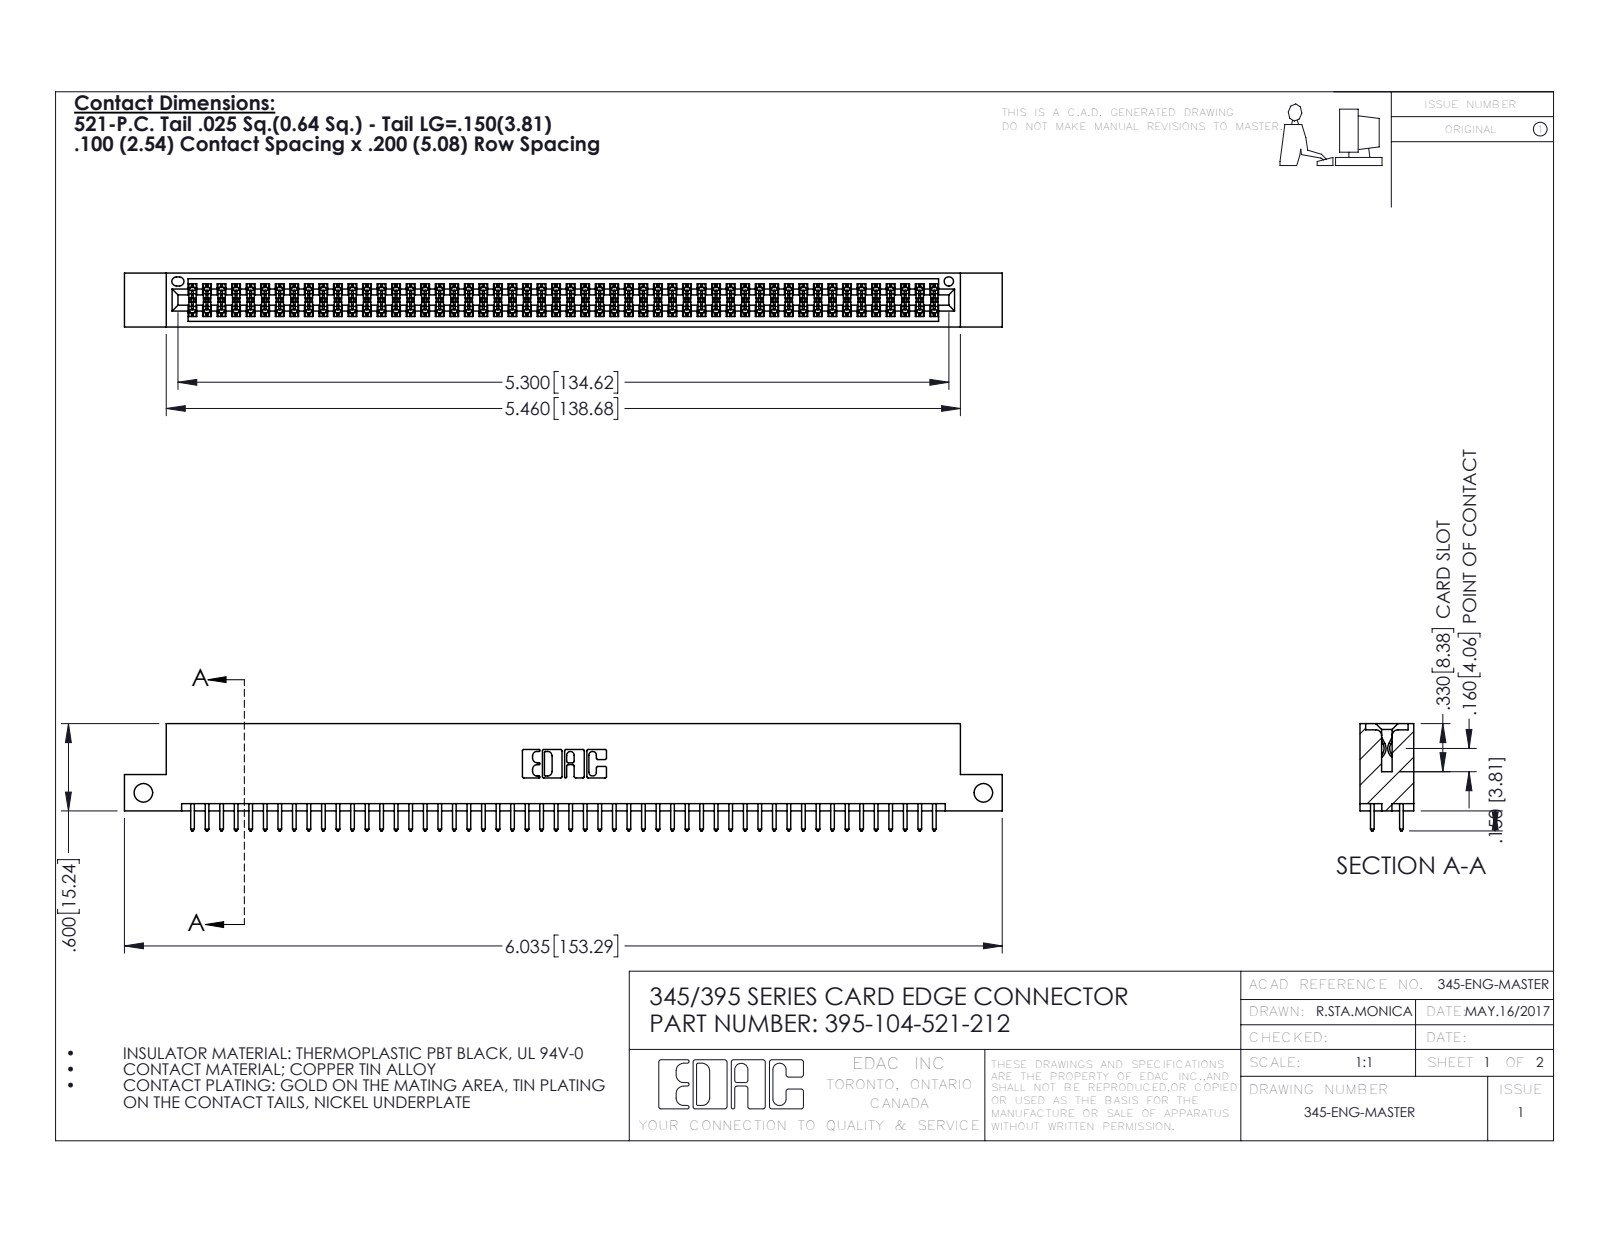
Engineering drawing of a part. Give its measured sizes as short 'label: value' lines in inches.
name: 395-104-521-212; 345-292-001_345-293-121; 345 Part_Flush Mounting Lugs - Side Mount
written by: SolidWorks 2016 (CONFIG_CONTROL_DESIGN)
unit: in
bodies: 105 solids, 5326 faces (3512 planar, 1814 cylindrical, 0 other)
size: 6.035 × 0.737 × 0.37
volume: 0.906 in³; area: 33.69 in²
holes: 2× ⌀0.128, 1× ⌀0.064
rounds: 156× R0.006, 104× R0.01, 22× R0.01, 6× R0.007, 6× R0.031, 3× R0.026, 2× R0.014, 2× R0.019
face distances: 0.298, 0.072, 0.2, 0.098, 0.272, 0.025, 0.37, 0.225, 0.175, 0.149
hole spacings: 5.775
